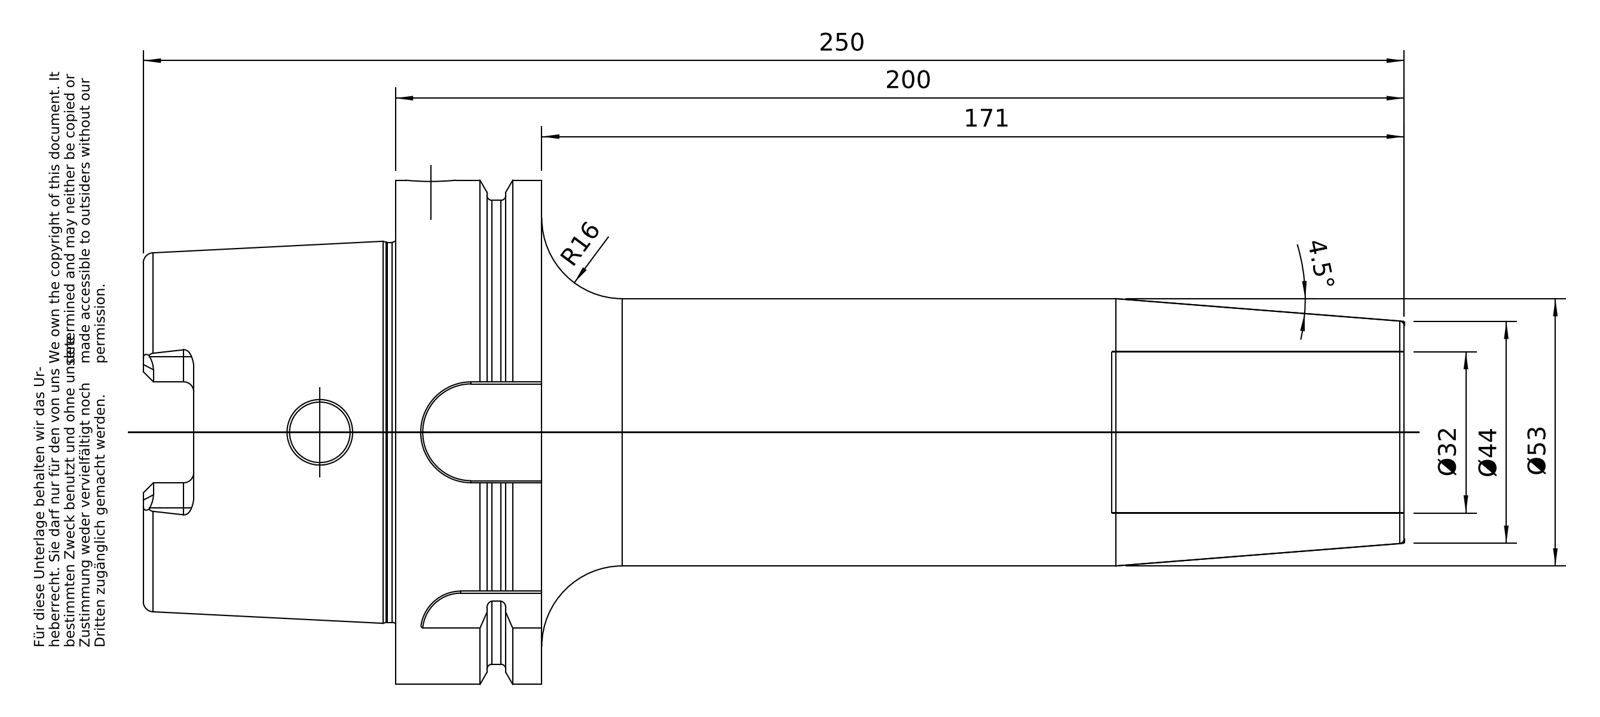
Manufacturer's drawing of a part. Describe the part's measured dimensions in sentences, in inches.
The part is named "A100-146-32". Its 3-D file was written by "PRO/ENGINEER BY PARAMETRIC TECHNOLOGY CORPORATION, 2010430 (CONFIG_CONTROL_DESIGN)". It is 1 solid with 174 faces: 50 planar, 51 cylindrical and 73 other. Overall it measures 9.843 by 3.937 by 3.937 inches. Its volume is 35.09 cubic inches and its surface area 127.1 square inches. Round holes: 1 of diameter 0.394, 1 of diameter 0.472, 1 of diameter 0.886, 1 of diameter 0.945, 1 of diameter 0.957, 1 of diameter 0.965, 1 of diameter 1.26, 1 of diameter 2.087, 1 of diameter 2.48. Round bosses or shafts: 1 of diameter 3.937, 1 of diameter 3.622, 1 of diameter 2.967. Partial cylindrical surfaces (rounded edges, fillets, slot ends): 6 of radius 0.079, 4 of radius 0.197, 1 of radius 0.315, 1 of radius 0.394, 1 of radius 0.433. The main face-to-face distances are 1.142, 0.492, 0.65, 1.969, 2.461, 3.11, 7.559, 5.591, 5.098, 4.449.
